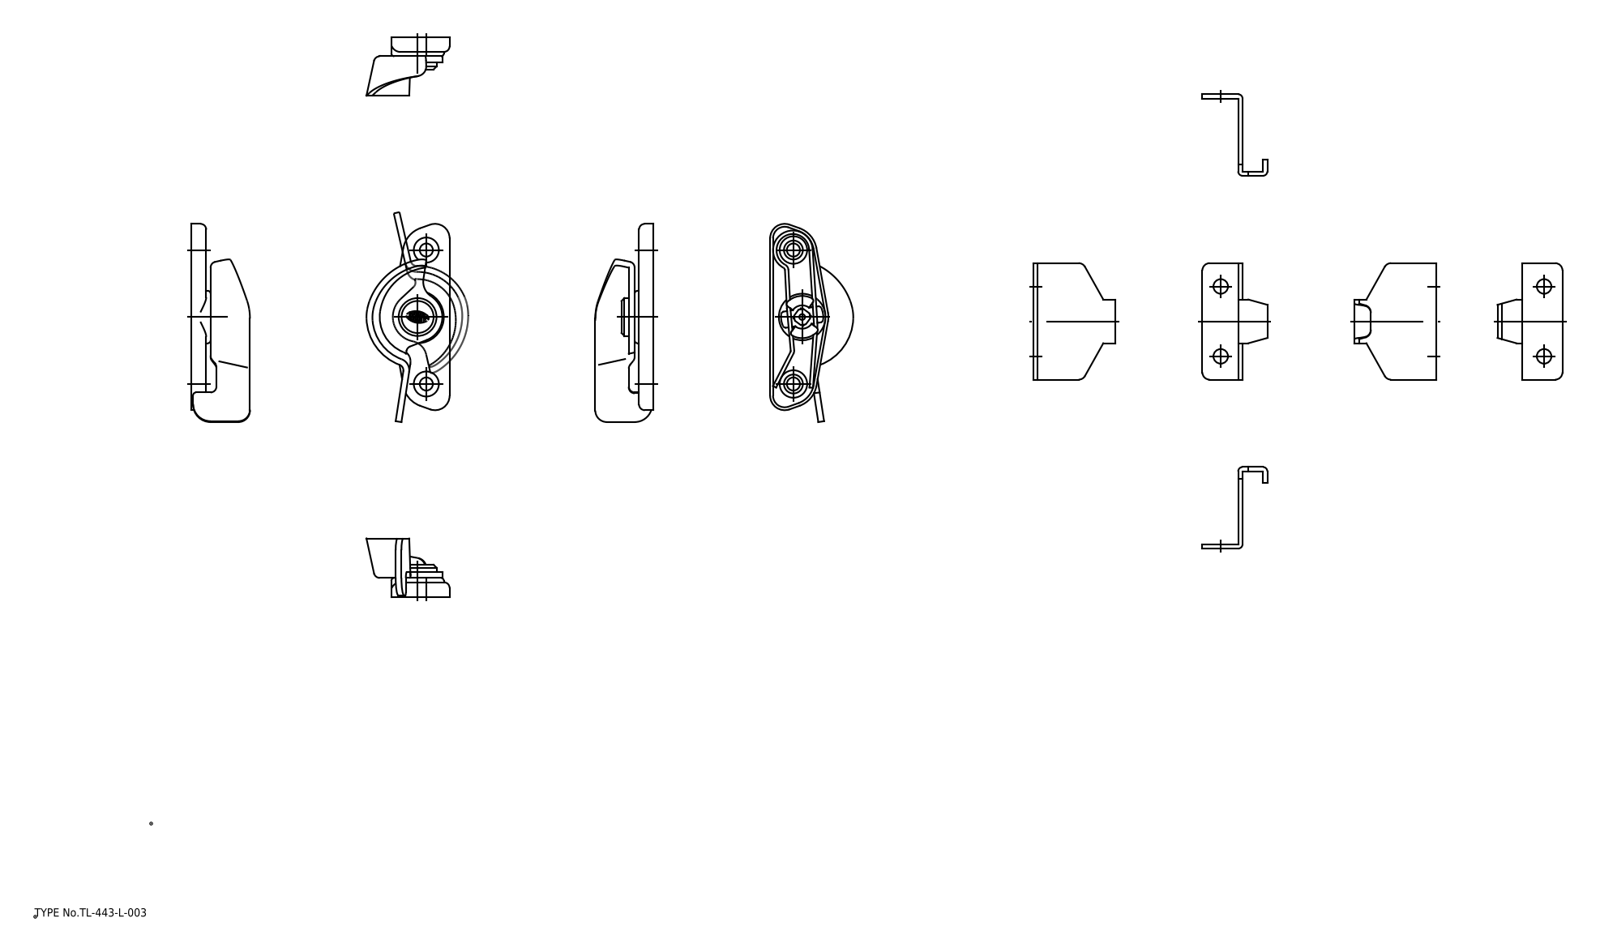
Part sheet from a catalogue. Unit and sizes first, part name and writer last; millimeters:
Units: millimetres
Overall size (bounding box): 68.08 × 53.35 × 28
Round holes (diameter × count): ⌀5 ×2, ⌀9.3 ×1, ⌀16 ×1
Round bosses / shafts (diameter × count): ⌀1.2 ×5, ⌀18 ×1, ⌀13 ×1
Partial cylindrical surfaces — rounded edges, fillets, slot ends (radius × count): R1 ×14, R2 ×9, R4 ×4, R1.5 ×3, R5 ×3, R3 ×2, R6 ×2, R8 ×2
Main face-to-face distances: 1.5, 1, 13, 12, 14.5, 2.5, 2, 11.5, 13.5, 10.5
Hole centre spacings: 31.85, 24
Volume: 7 030 mm³ · Surface area: 10 380 mm²
Bodies: 4 solids, 216 faces (78 planar, 72 cylindrical, 66 other)
Part name (STEP PRODUCT): レバー; ベース; スプリング; キーパー
STEP written by: spGate 19.8.4 (****-****-****-****) (AUTOMOTIVE_DESIGN)
